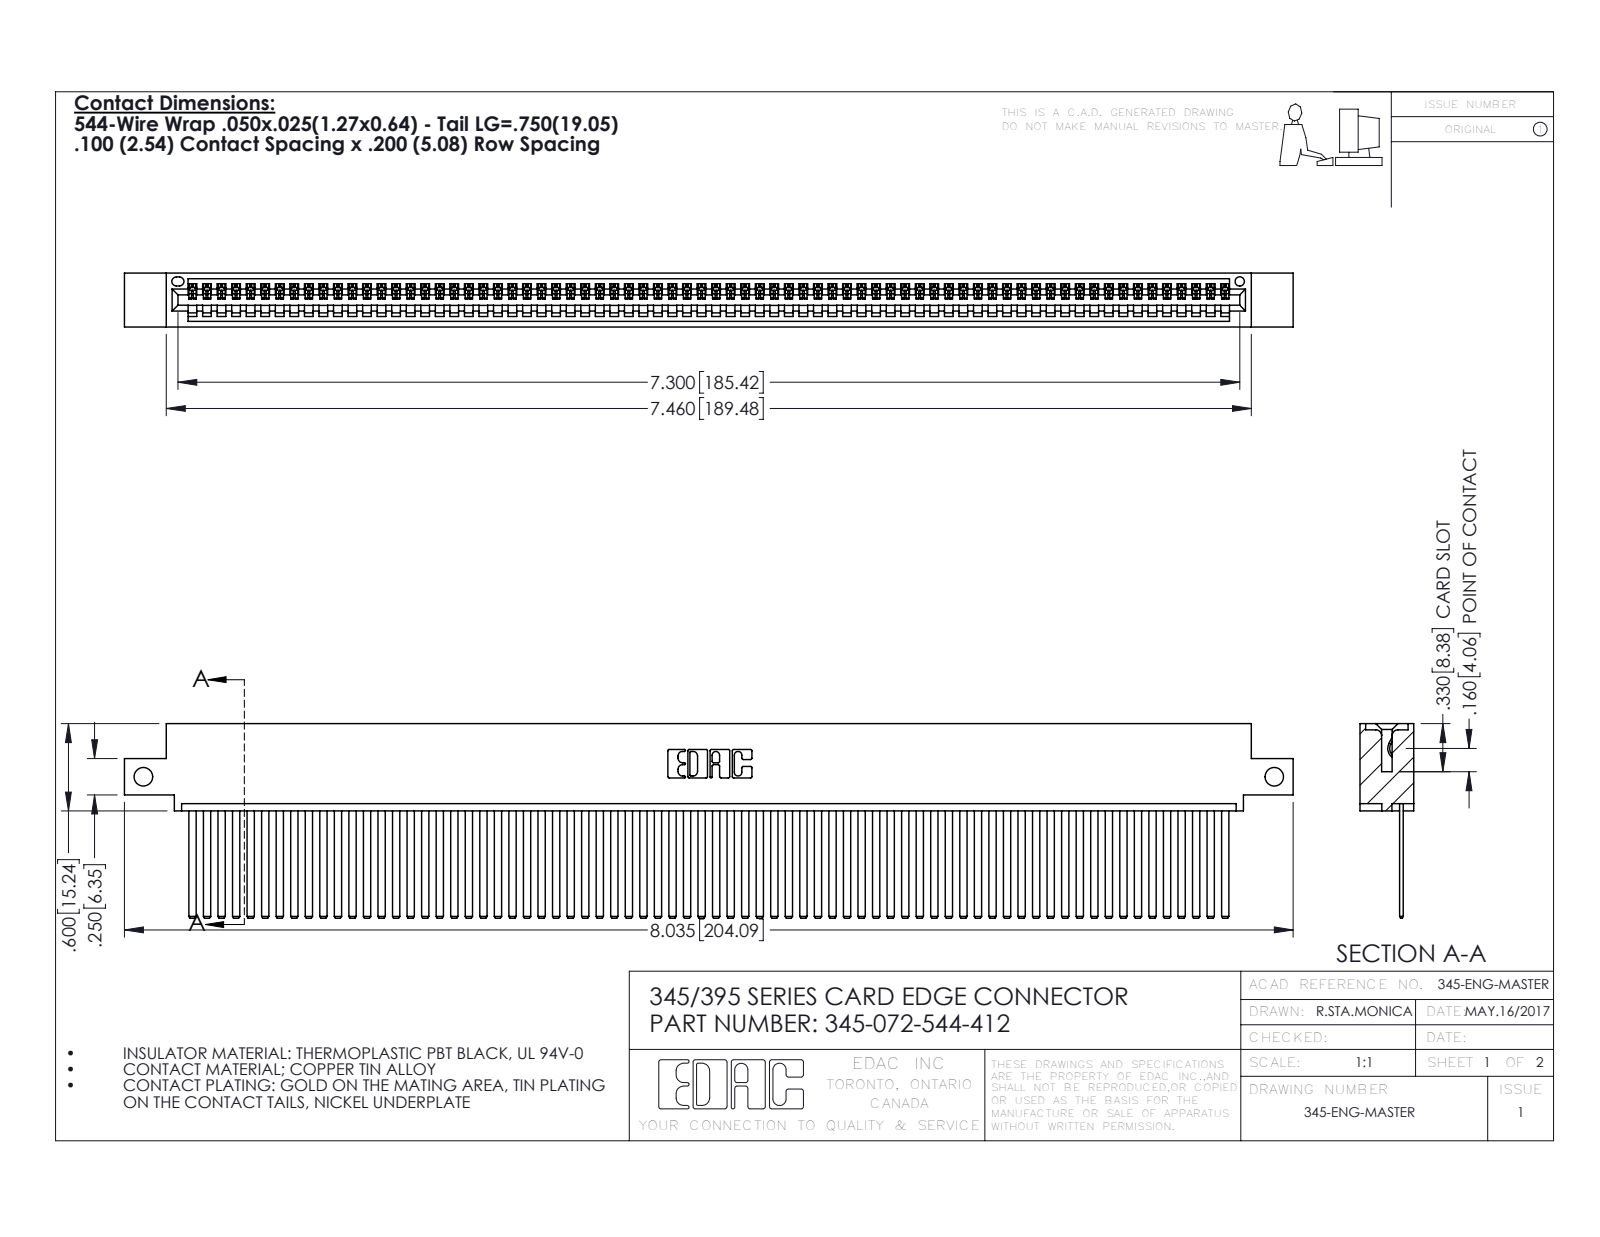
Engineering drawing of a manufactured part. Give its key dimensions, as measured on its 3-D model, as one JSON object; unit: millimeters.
{"part_name": "345-072-544-412; 345-292-001_345-293-144; 345 Part_0.110 Offset - Side Mount", "step_written_by": "SolidWorks 2016 (CONFIG_CONTROL_DESIGN)", "units": "millimeters", "bodies": {"solids": 73, "faces": 3874, "planar": 2676, "cylindrical": 1198, "other": 0}, "overall_size": [204.1, 34, 9.4], "volume_mm3": 20300, "surface_area_mm2": 29830, "round_holes": [[3.3, 2], [1.6, 1]], "partial_cylinders_radius": [[0.2, 144], [0.3, 22], [0.2, 6], [0.8, 6], [0.7, 3], [0.8, 2], [1, 2], [0.4, 1]], "face_to_face_distances": [1.8, 7.6, 0.6, 2.5, 6.9, 9.4, 5.1, 5.7, 3.8, 1.8], "hole_center_spacings": [197.5]}
